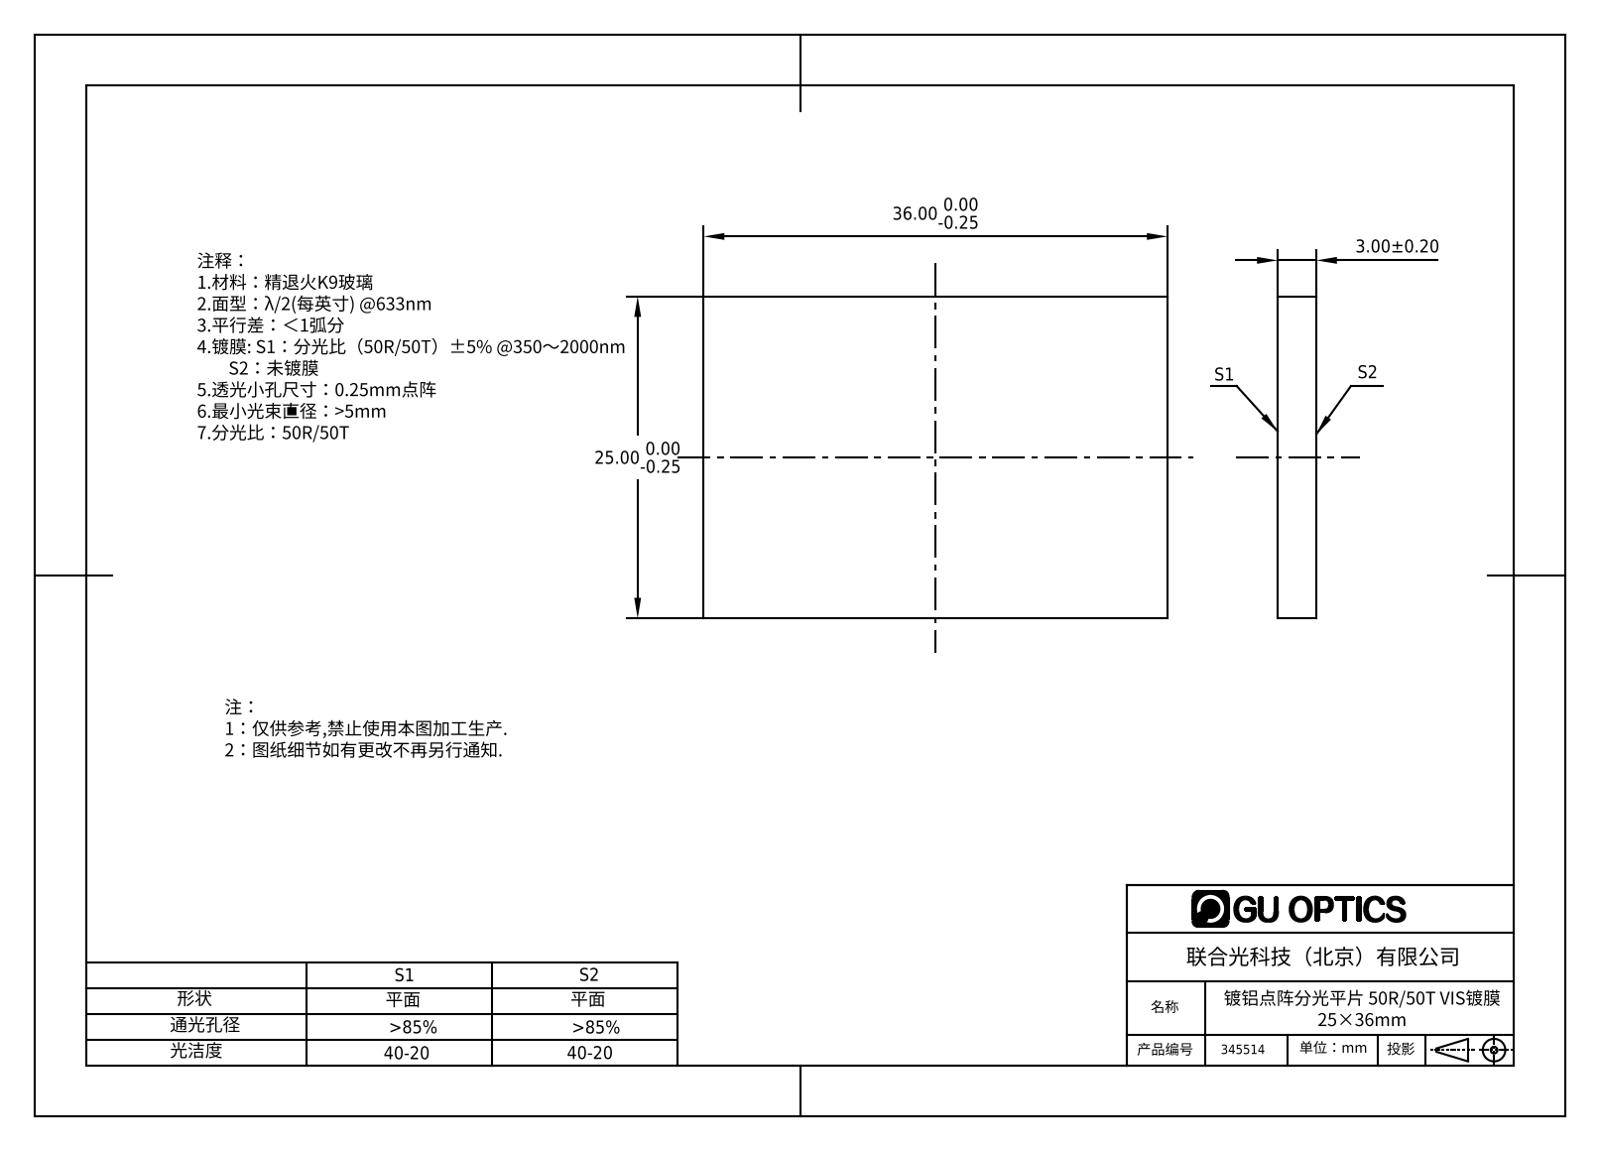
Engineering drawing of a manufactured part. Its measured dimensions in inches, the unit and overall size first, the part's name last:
Units: inches
Overall size (bounding box): 1.417 × 0.984 × 0.118
Main face-to-face distances: 0.118, 0.984, 1.417
Volume: 0.165 in³ · Surface area: 3.357 in²
Bodies: 1 solid, 6 faces (6 planar, 0 cylindrical, 0 other)
Part name (STEP PRODUCT): 345505
STEP written by: SolidWorks 2016 (AUTOMOTIVE_DESIGN)
